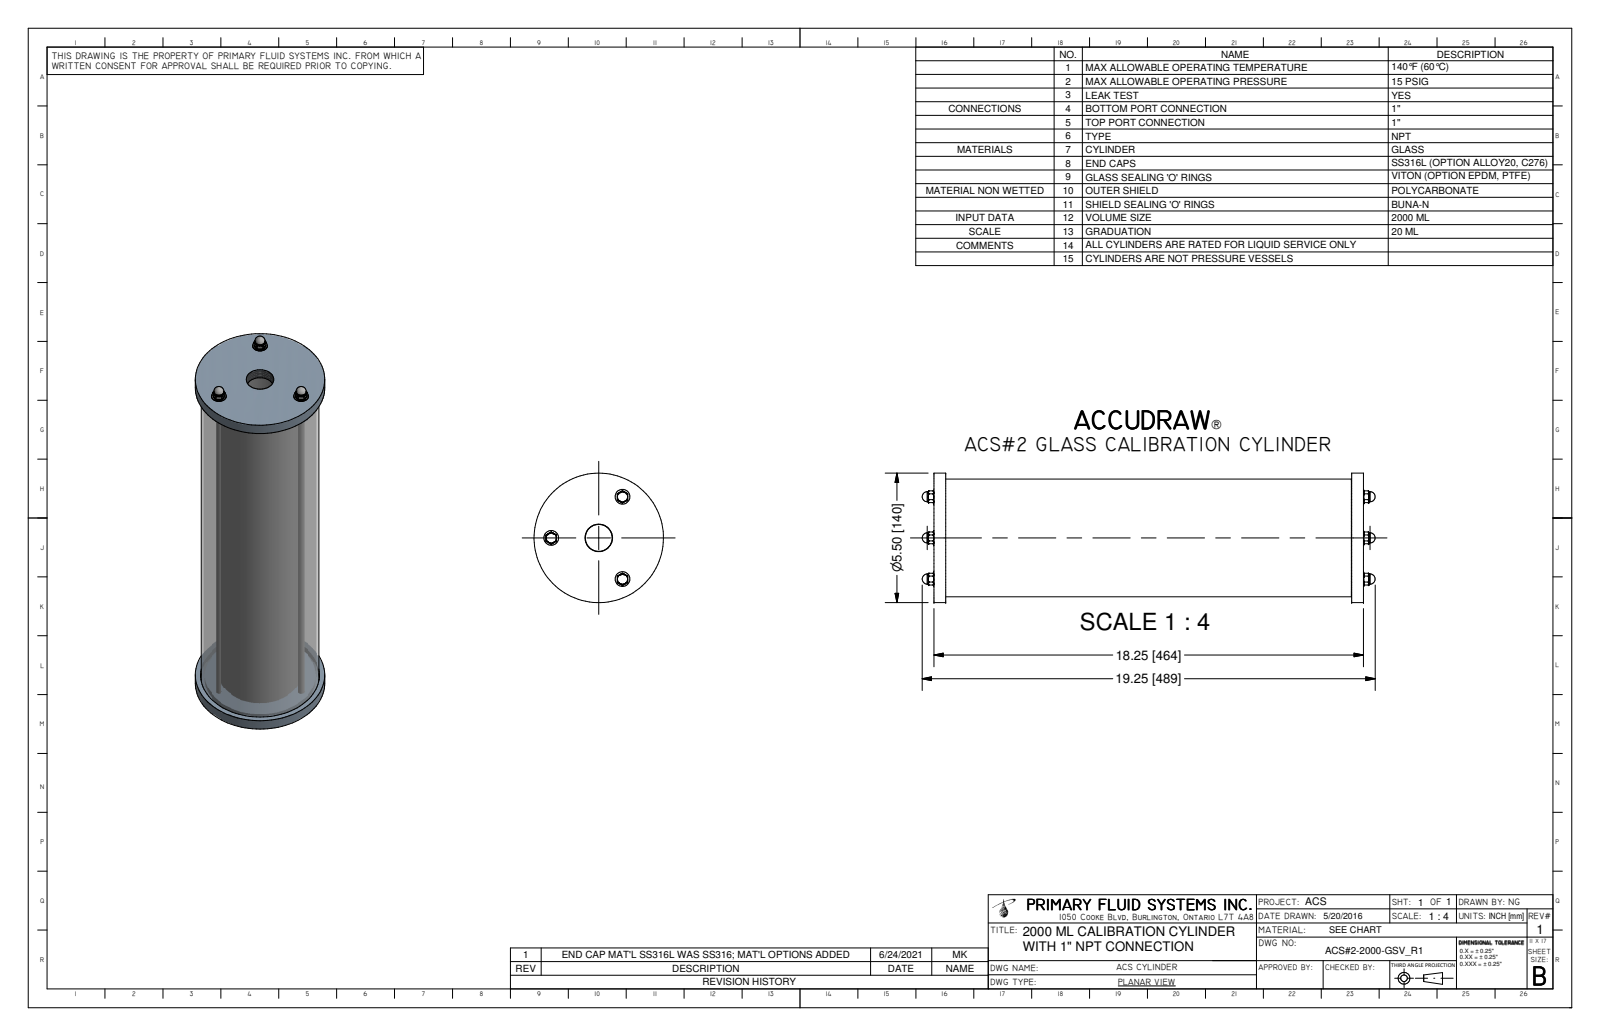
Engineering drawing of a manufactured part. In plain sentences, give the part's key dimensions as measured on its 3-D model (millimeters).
The part is named "ACS#2-2000-GSV_R0; ACS-3-2000-METAL_R3; ACS-2-2000-PC_R6; ACS-1-2000-A_R0 (+3 more)". Its 3-D file was written by "Autodesk Inventor 2009 (AUTOMOTIVE_DESIGN)". It is 19 solids with 425 faces: 38 planar, 41 cylindrical and 346 other. Overall it measures 489 by 139.7 by 139.7 millimeters. Its volume is 1 214 000 cubic millimeters and its surface area 712 300 square millimeters. Round holes: 3 of diameter 4.6, 3 of diameter 6.8, 3 of diameter 7.1, 1 of diameter 80, 1 of diameter 86.4, 1 of diameter 120.7, 1 of diameter 128.3. Round bosses or shafts: 3 of diameter 15.9, 3 of diameter 6.4, 1 of diameter 139.7, 1 of diameter 127, 1 of diameter 119.4, 1 of diameter 85, 1 of diameter 78.7. The main face-to-face distances are 12.7, 450.9, 463.6, 438.2, 5.7, 457.8, 7, 445.1, 2.5, 454.7. The hole center spacings are 51.3, 88.8.
